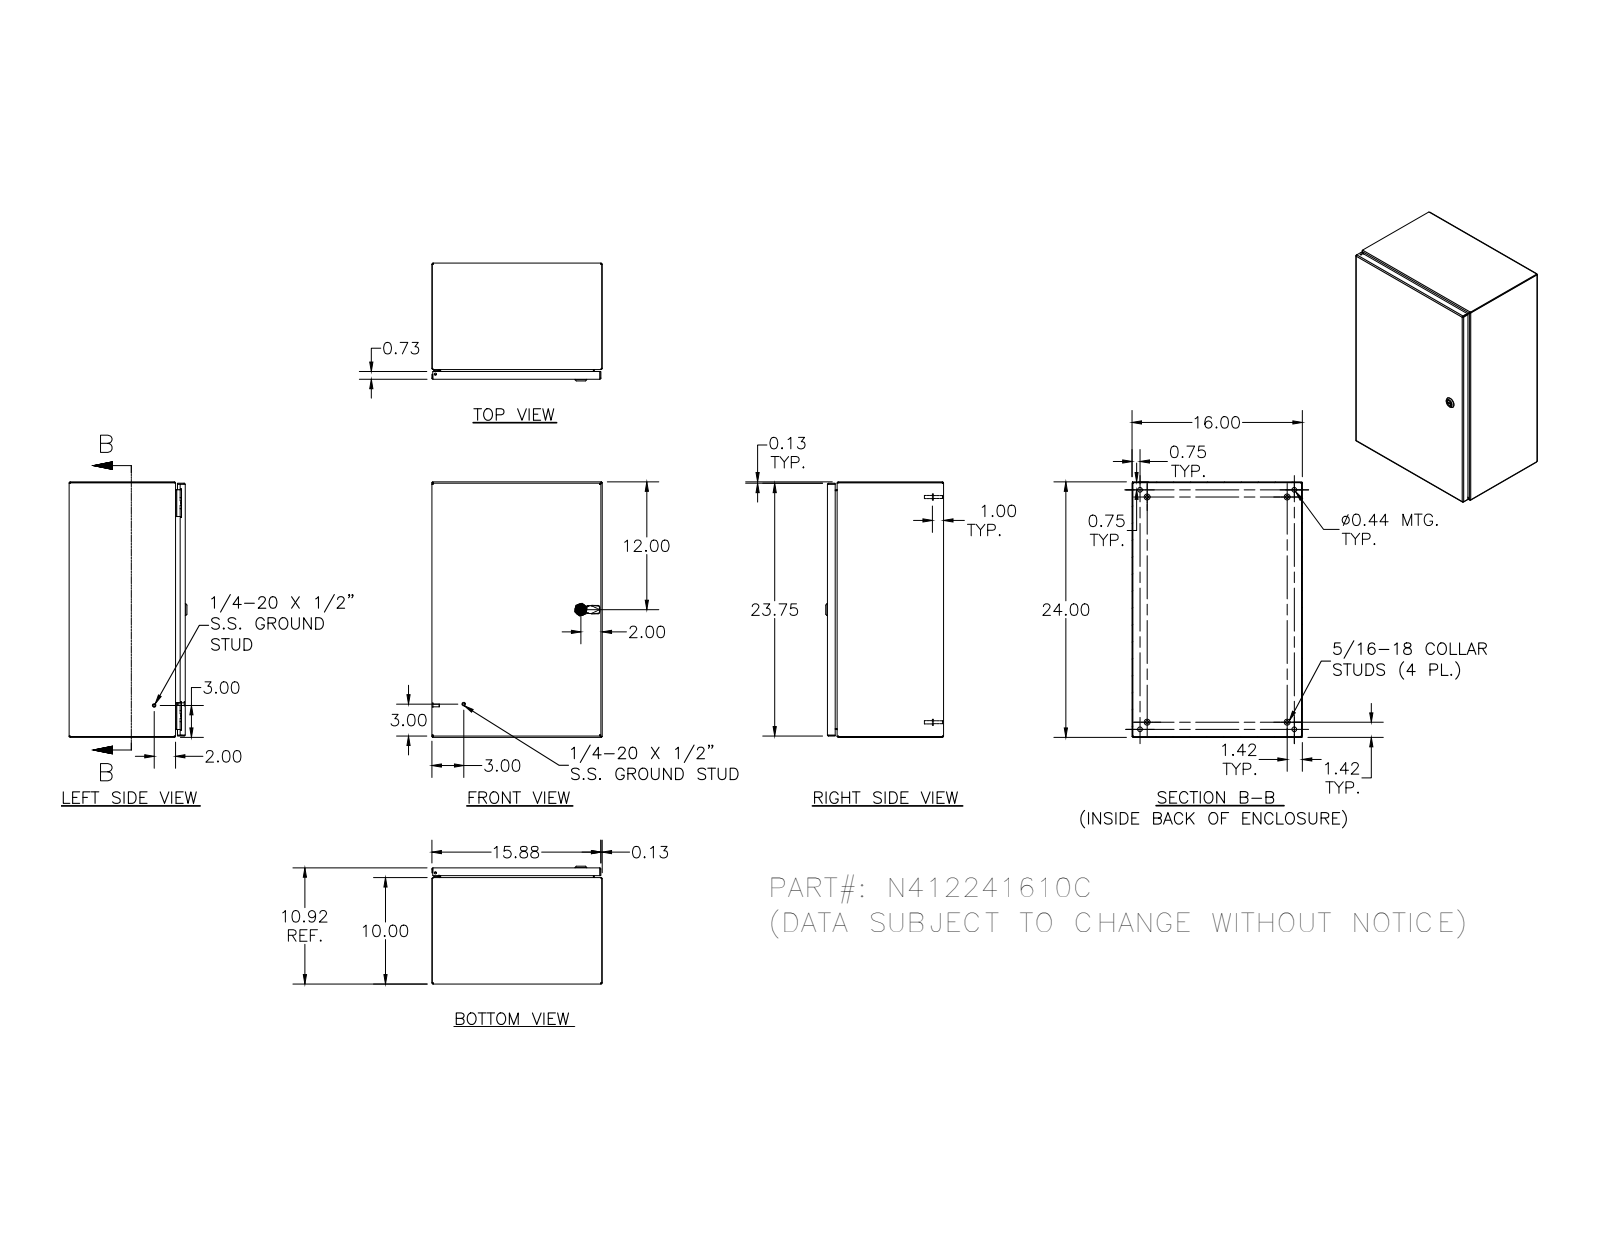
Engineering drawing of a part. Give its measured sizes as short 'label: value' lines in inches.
name: N412241610C
written by: SolidWorks 2018 (AUTOMOTIVE_DESIGN)
unit: in
bodies: 33 solids, 1449 faces (530 planar, 547 cylindrical, 372 other)
size: 24 × 16 × 11.075
volume: 128 in³; area: 3 479 in²
holes: 5× ⌀0.188, 4× ⌀0.093, 4× ⌀0.152, 4× ⌀0.167, 4× ⌀0.172, 4× ⌀0.437, 2× ⌀0.156, 1× ⌀0.187, 1× ⌀0.197, 1× ⌀0.315, 1× ⌀0.394, 1× ⌀0.402
bosses: 10× ⌀0.25, 4× ⌀0.563, 4× ⌀0.36, 4× ⌀0.32, 4× ⌀0.3, 4× ⌀0.256, 4× ⌀0.164, 4× ⌀0.131
rounds: 30× R0.012, 30× R0.031, 26× R0.05, 20× R0.105, 18× R0.016, 16× R0.125, 13× R0.02, 8× R0.032
face distances: 0.074, 10.843, 0.074, 10.769, 10.917, 15.926, 15.852, 15.926, 16, 23.852
hole spacings: 20, 0.66, 0.656, 1.307, 1.965, 0.5, 0.984, 1.311
